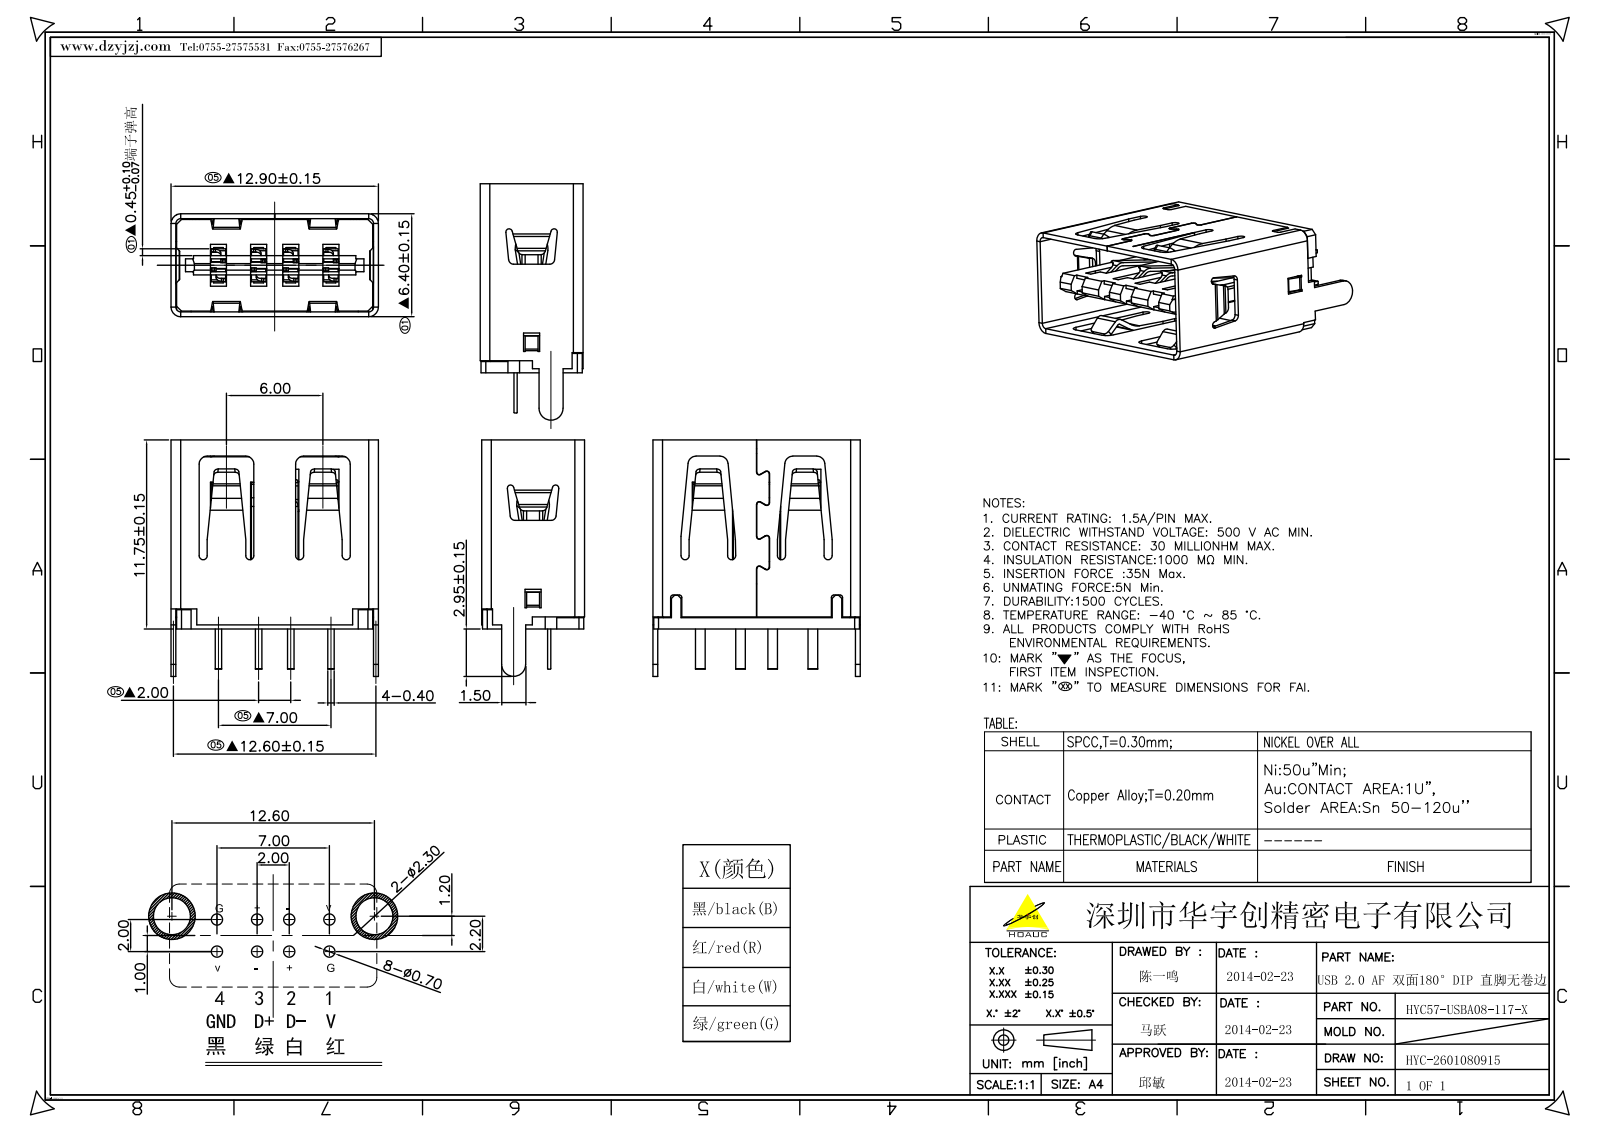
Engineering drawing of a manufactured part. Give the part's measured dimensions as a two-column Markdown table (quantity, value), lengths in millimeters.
| quantity | value |
| --- | --- |
| STEP written by | CREO PARAMETRIC BY PTC INC, 2022073 (AUTOMOTIVE_DESIGN) |
| units | millimeters |
| bodies | 2 solids, 509 faces (369 planar, 132 cylindrical, 8 other) |
| overall size | 14.7 × 12.9 × 6.4 |
| volume | 422 mm³ |
| surface area | 1 357 mm² |
| partial cylindrical surfaces (radius × count) | 0.5 × 16, 0.15 × 12, 0.25 × 12, 0.3 × 12, 0.6 × 12, 0.17 × 8, 0.2 × 8, 0.1 × 2 |
| main face-to-face distances | 6.1, 2.3, 3.8, 2.6, 3.5, 12.6, 5.8, 6.4, 0.35, 1.2 |
